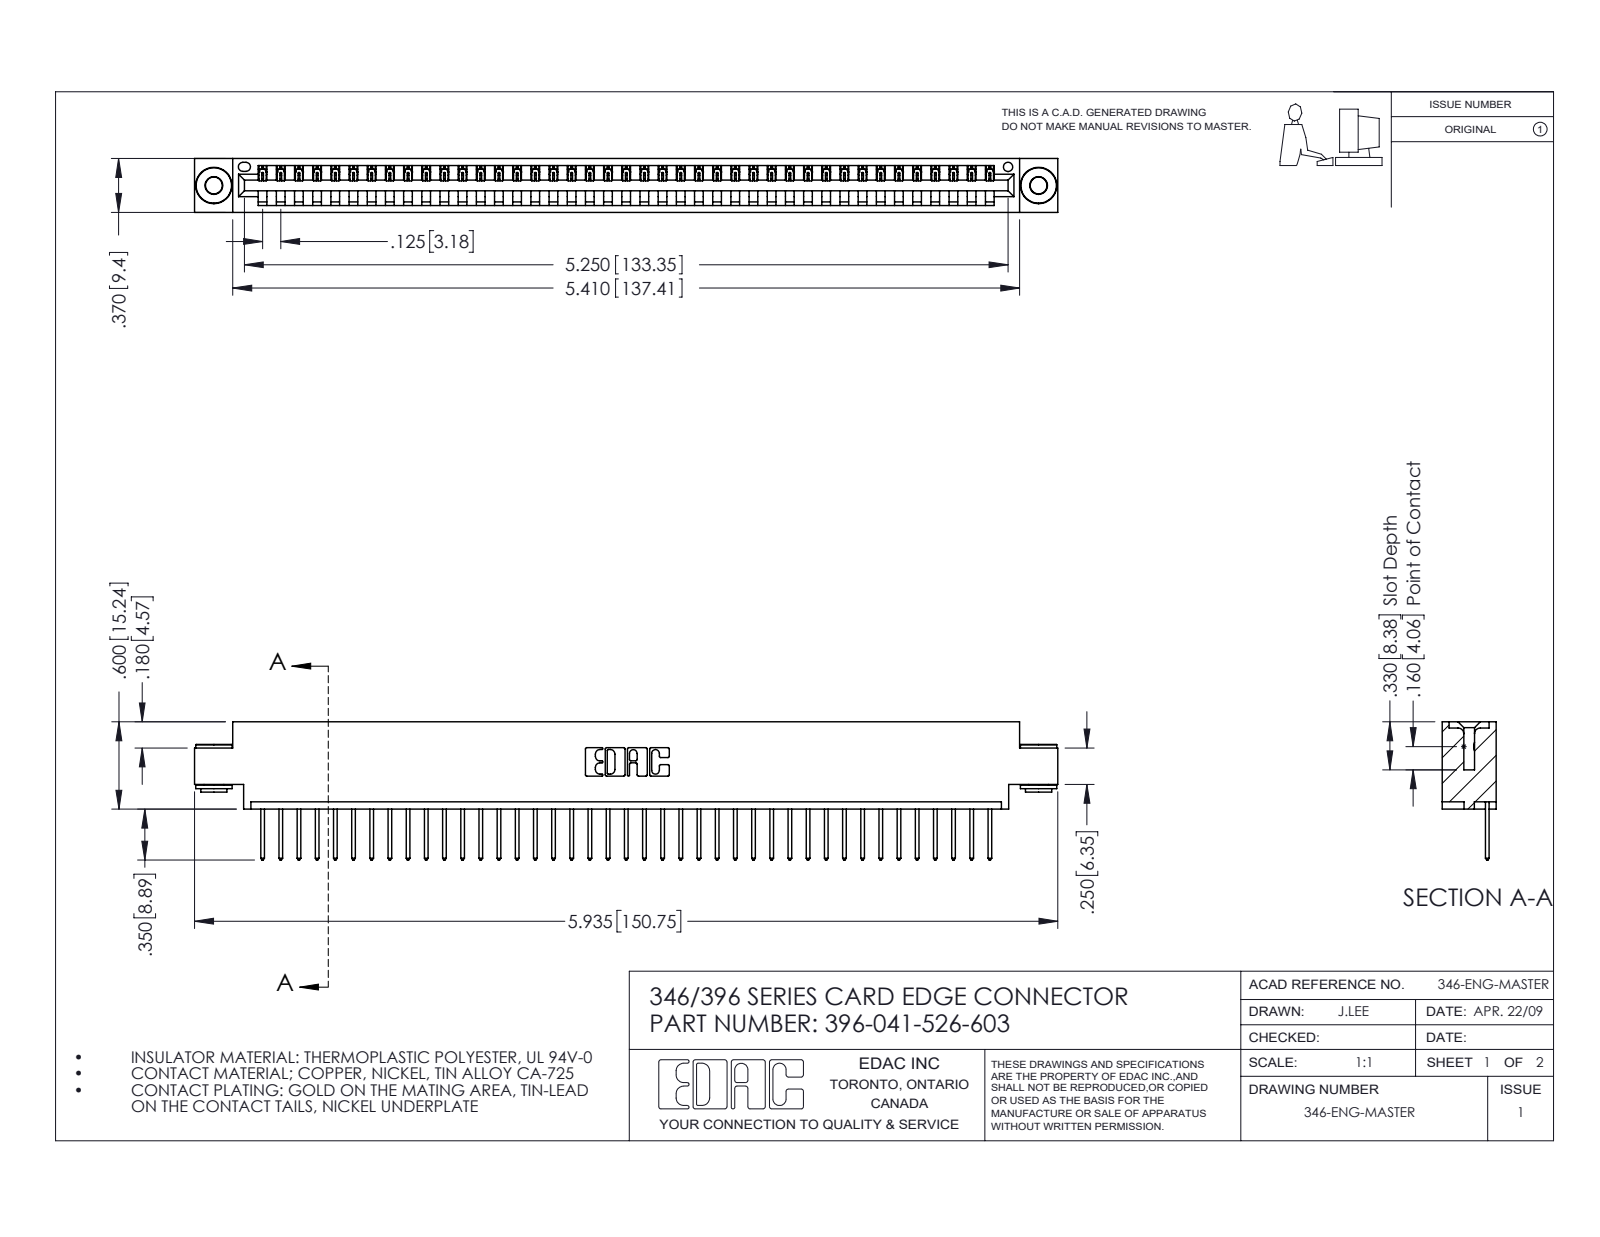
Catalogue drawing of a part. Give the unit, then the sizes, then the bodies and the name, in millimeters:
Units: millimetres
Overall size (bounding box): 150.7 × 24.1 × 9.4
Round holes (diameter × count): ⌀2.9 ×2, ⌀4 ×2, ⌀1.6 ×1
Round bosses / shafts (diameter × count): ⌀6.4 ×2, ⌀4.6 ×2, ⌀3.5 ×2
Partial cylindrical surfaces — rounded edges, fillets, slot ends (radius × count): R0.2 ×82, R0.3 ×82, R0.3 ×22, R0.2 ×6, R0.8 ×6, R0.7 ×3, R0.8 ×2, R1 ×2
Main face-to-face distances: 1.2, 8.2, 9.4, 6.4, 0.6, 1.8, 7.6, 3.8, 5.6, 2.5
Hole centre spacings: 6.2, 138.7, 144
Volume: 14 300 mm³ · Surface area: 18 150 mm²
Bodies: 44 solids, 2542 faces (1730 planar, 804 cylindrical, 8 other)
Part name (STEP PRODUCT): 396-041-526-603; 346 Part_0.170 Offset - 0.156 Dia-TH; 345-250-002_345-250-002-102; 345-292-001_345-293-126
STEP written by: SolidWorks 2016 (CONFIG_CONTROL_DESIGN)
